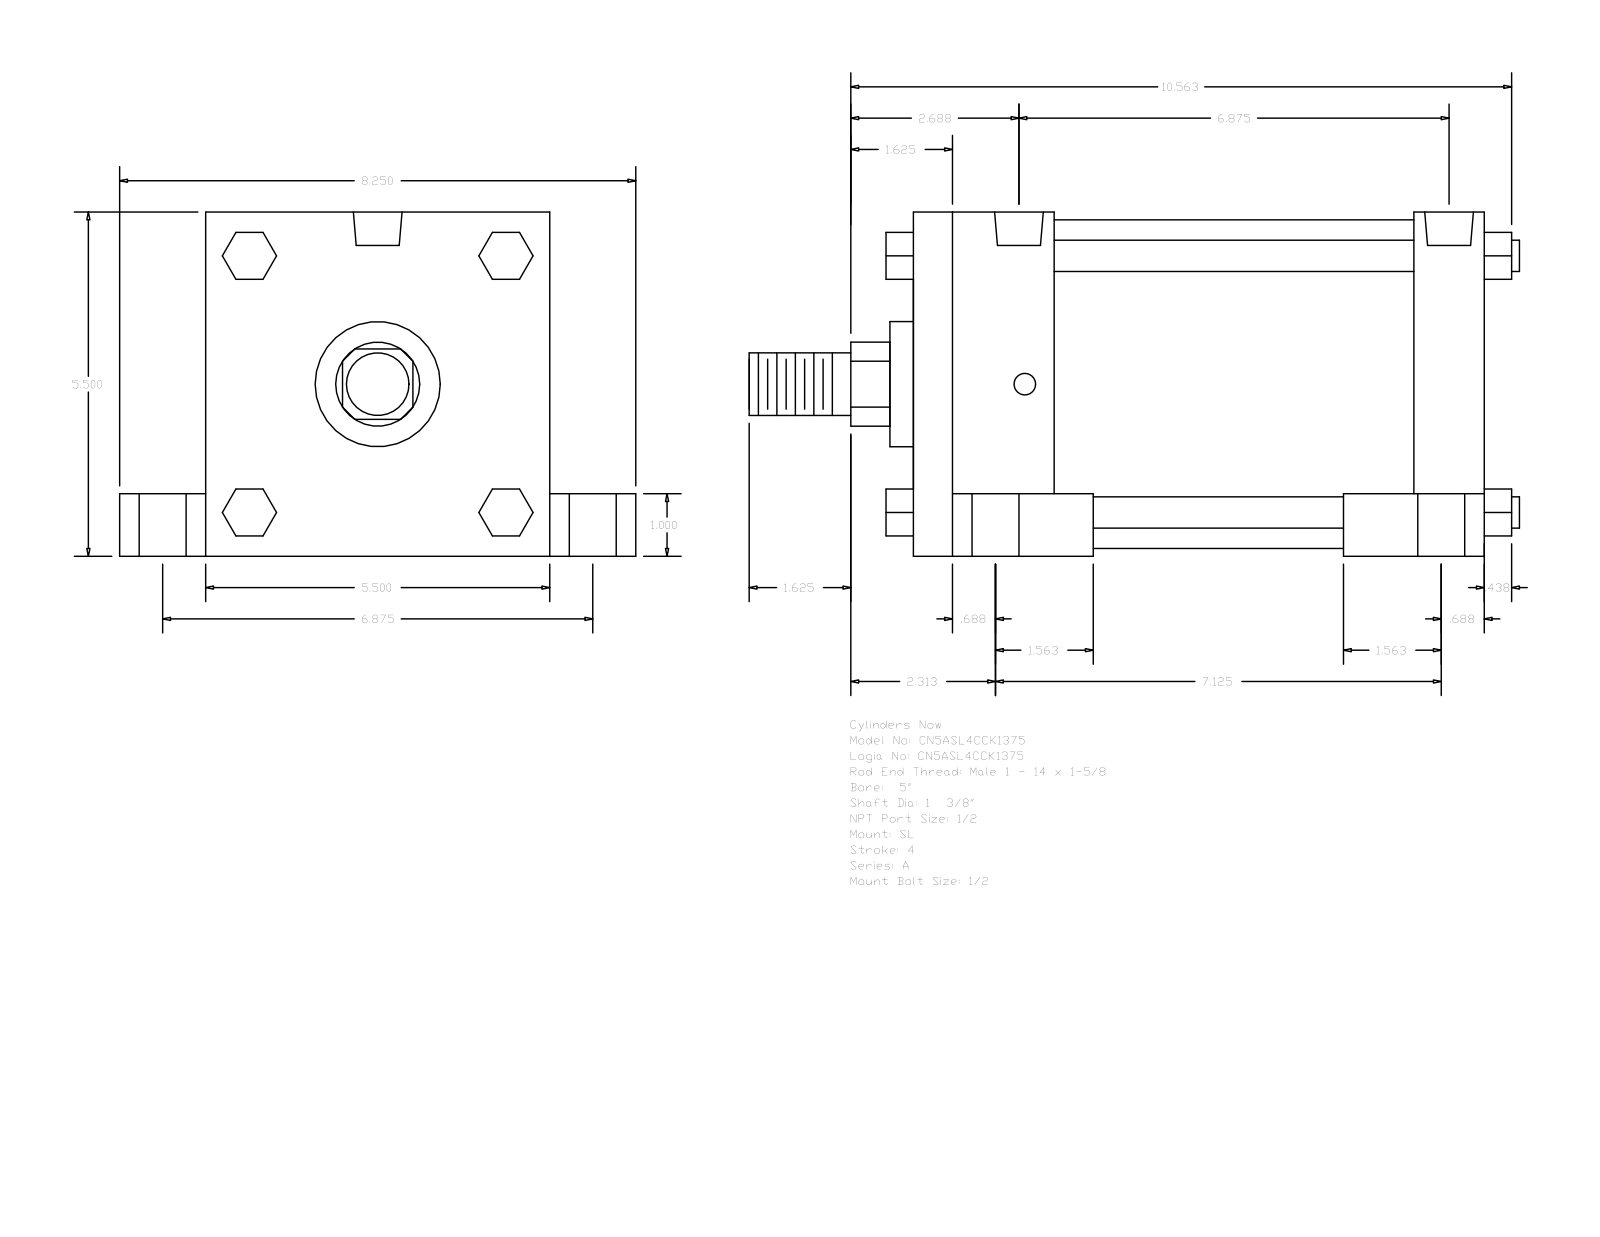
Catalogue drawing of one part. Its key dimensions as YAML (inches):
part_name: "A_SL__0500_1.375"
step_written_by: "GSSL Pune (CONFIG_CONTROL_DESIGN)"
units: inches
bodies: {solids: 0, faces: 150, planar: 114, cylindrical: 36, other: 0}
overall_size: [12.313, 8.25, 5.5]
round_holes:
  - {diameter: 0.344, count: 4}
  - {diameter: 0.75, count: 4}
  - {diameter: 1, count: 4}
  - {diameter: 0.778, count: 2}
round_bosses_or_shafts:
  - {diameter: 0.5, count: 4}
  - {diameter: 5.25, count: 1}
  - {diameter: 2, count: 1}
  - {diameter: 1.375, count: 1}
  - {diameter: 1, count: 1}
partial_cylinders:
  - {radius: 0.672, count: 1}
face_to_face_distances: [5.5, 9.125, 6.875, 2.25, 1, 4.5, 1.375, 1.125, 8, 5.75]
hole_center_spacings: [0.094, 3.437, 3.44, 3.458, 3.469, 6.687, 6.781, 6.875]
